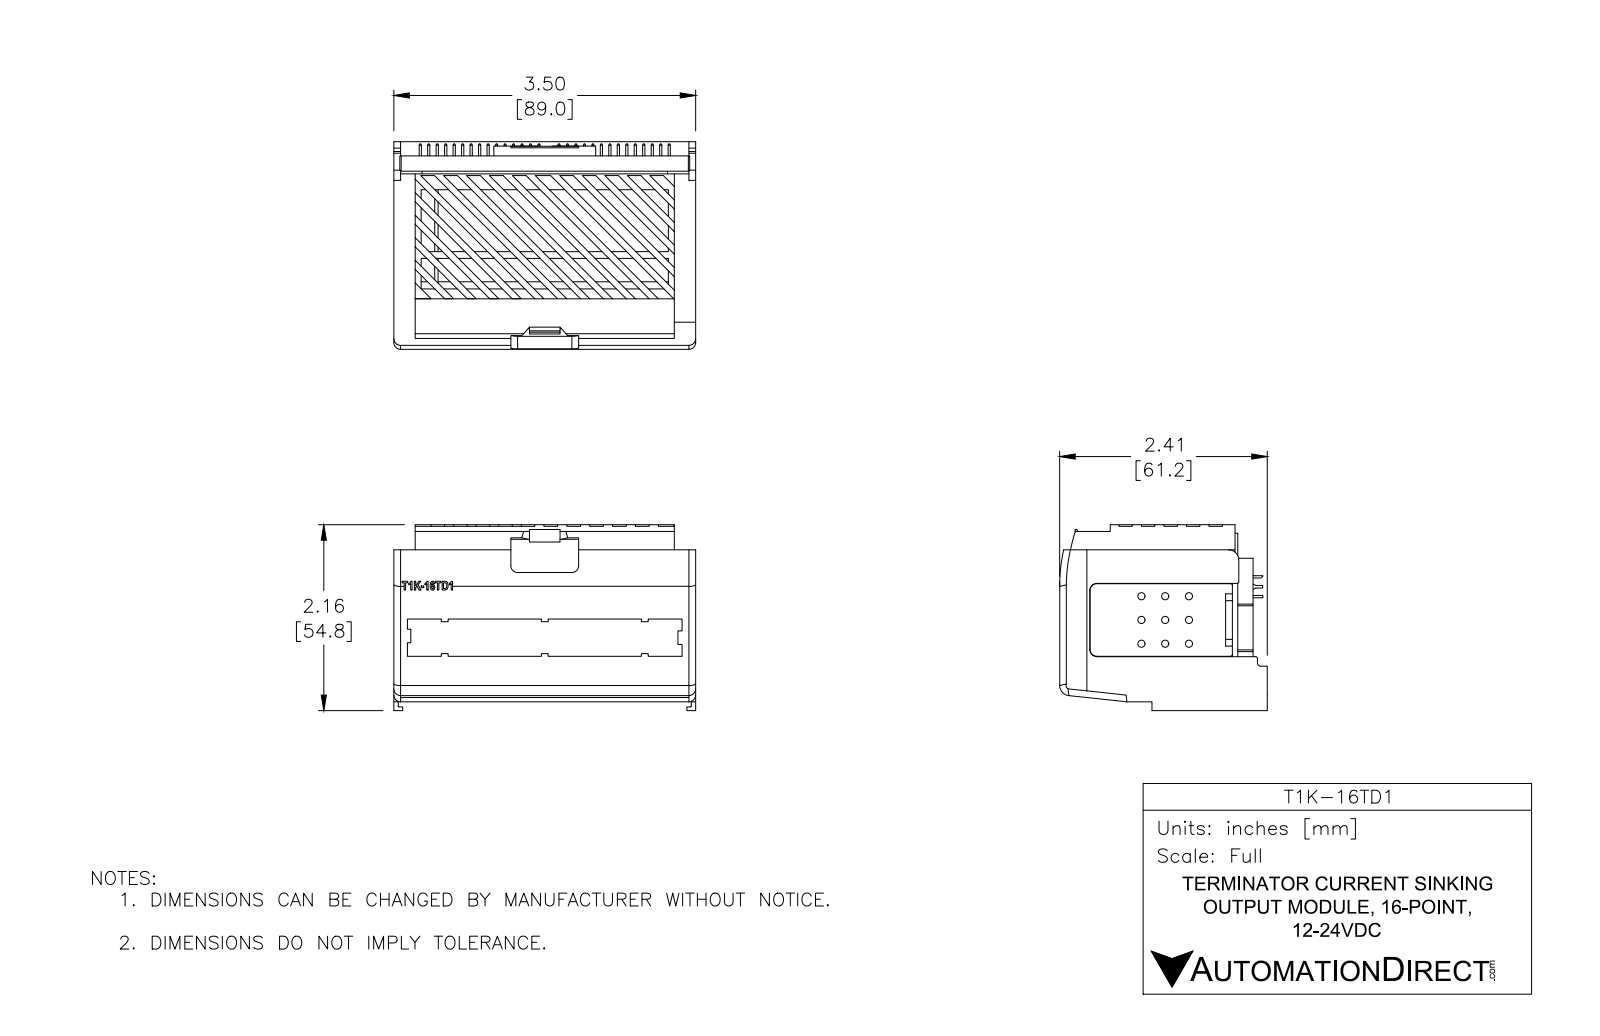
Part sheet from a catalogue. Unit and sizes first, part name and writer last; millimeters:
Units: millimetres
Overall size (bounding box): 88.7 × 65.1 × 61.36
Round holes (diameter × count): ⌀3 ×16
Round bosses / shafts (diameter × count): ⌀0.7 ×56
Partial cylindrical surfaces — rounded edges, fillets, slot ends (radius × count): R3.5 ×18, R1 ×5, R0.25 ×3, R0.55 ×3, R1.5 ×2, R8 ×1, R10 ×1, R18 ×1
Main face-to-face distances: 2, 86.7, 55.35, 0.5, 59.8, 88.7, 1.5, 55.26, 53.35, 84.7
Hole centre spacings: 5.15, 10.3, 15.45, 20.6, 25.75, 30.9, 36.05, 41.2
Volume: 45 450 mm³ · Surface area: 54 523 mm²
Bodies: 1 solid, 637 faces (441 planar, 181 cylindrical, 15 other)
Part name (STEP PRODUCT): T1K-16TD1
STEP written by: SolidWorks 2013 (AUTOMOTIVE_DESIGN)
